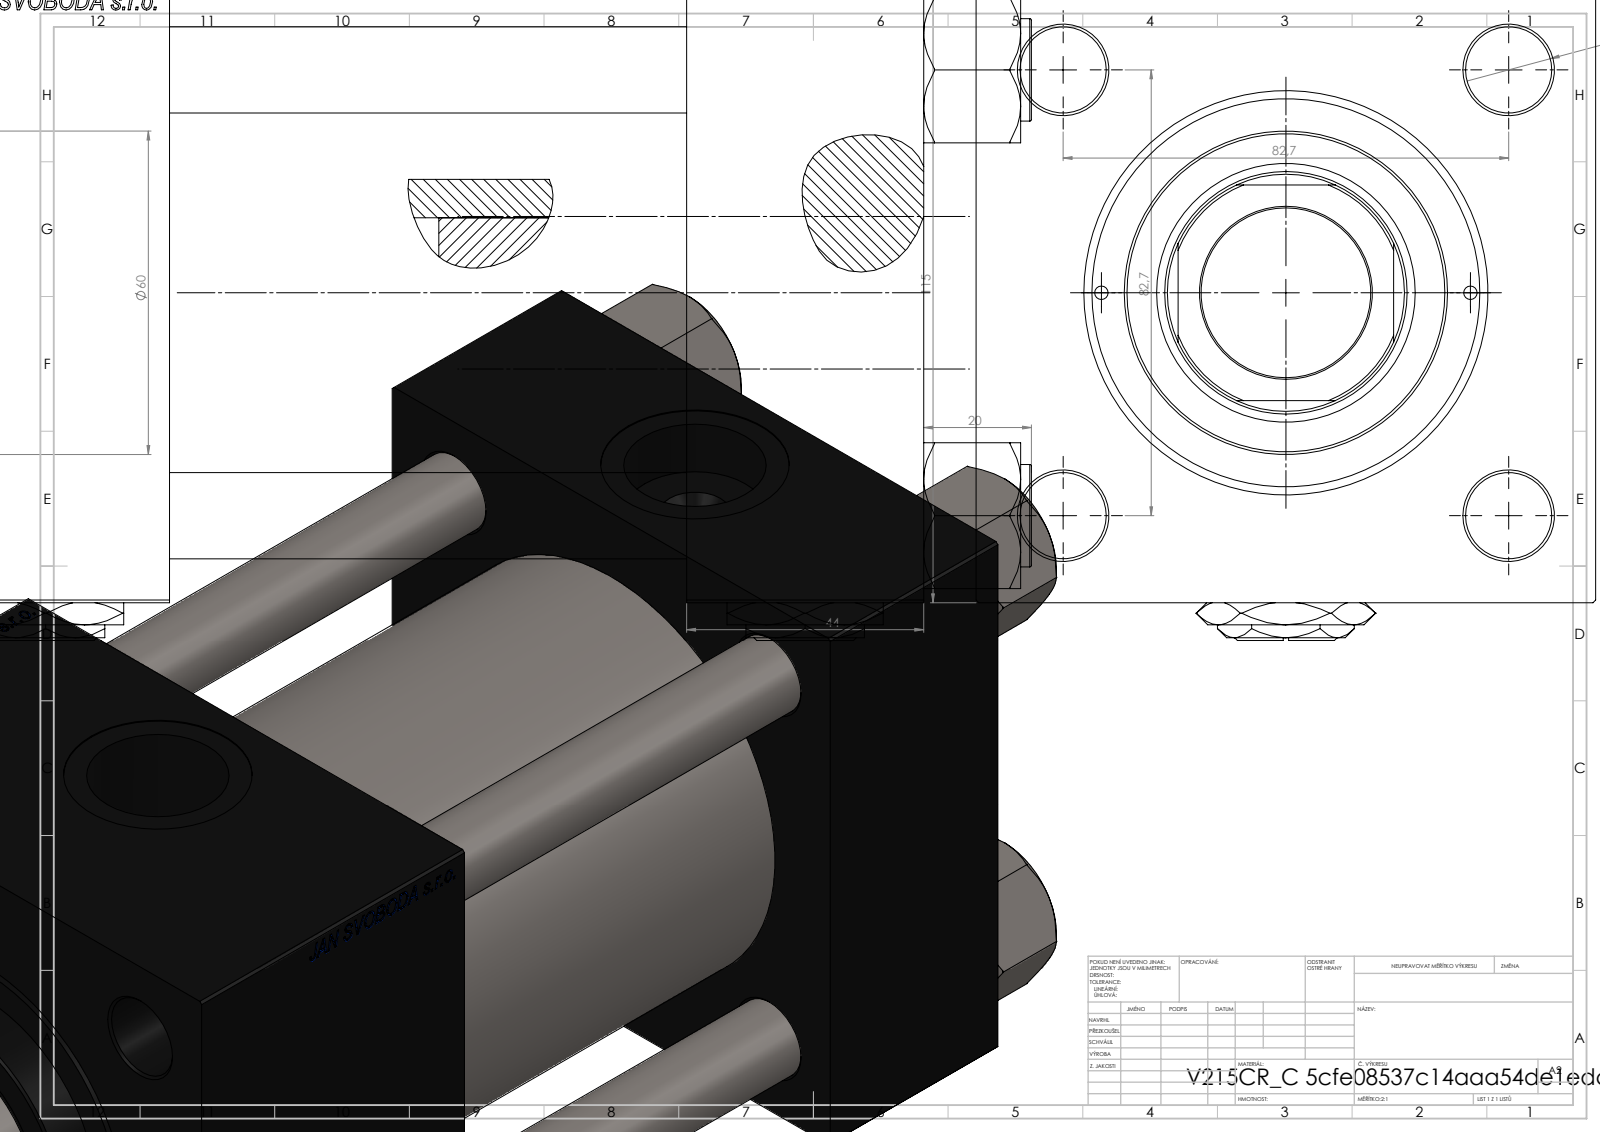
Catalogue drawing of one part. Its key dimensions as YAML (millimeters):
part_name: "V215CR_C_Body; V215_VC_A; V215CR_C_TYCINKA; V215CR_VCP_C (+2 more)"
step_written_by: "SolidWorks 2019 (CONFIG_CONTROL_DESIGN)"
units: millimeters
bodies: {solids: 13, faces: 1303, planar: 623, cylindrical: 102, other: 578}
overall_size: [260, 122, 115]
volume: 1900000
surface_area: 306942
round_holes:
  - {diameter: 16, count: 4}
  - {diameter: 2.5, count: 2}
  - {diameter: 7, count: 2}
  - {diameter: 26.44, count: 2}
  - {diameter: 35, count: 2}
  - {diameter: 31.5, count: 1}
  - {diameter: 45, count: 1}
  - {diameter: 48, count: 1}
  - {diameter: 61, count: 1}
  - {diameter: 72, count: 1}
  - {diameter: 80, count: 1}
round_bosses_or_shafts:
  - {diameter: 19, count: 4}
  - {diameter: 86, count: 1}
  - {diameter: 60, count: 1}
partial_cylinders:
  - {radius: 22, count: 1}
face_to_face_distances: [115, 44, 209, 165, 96, 69, 140, 180.3, 136.3, 40.3]
hole_center_spacings: [41.96, 58.48, 82.7, 86.17, 34.25, 116.96, 68.5, 141]
